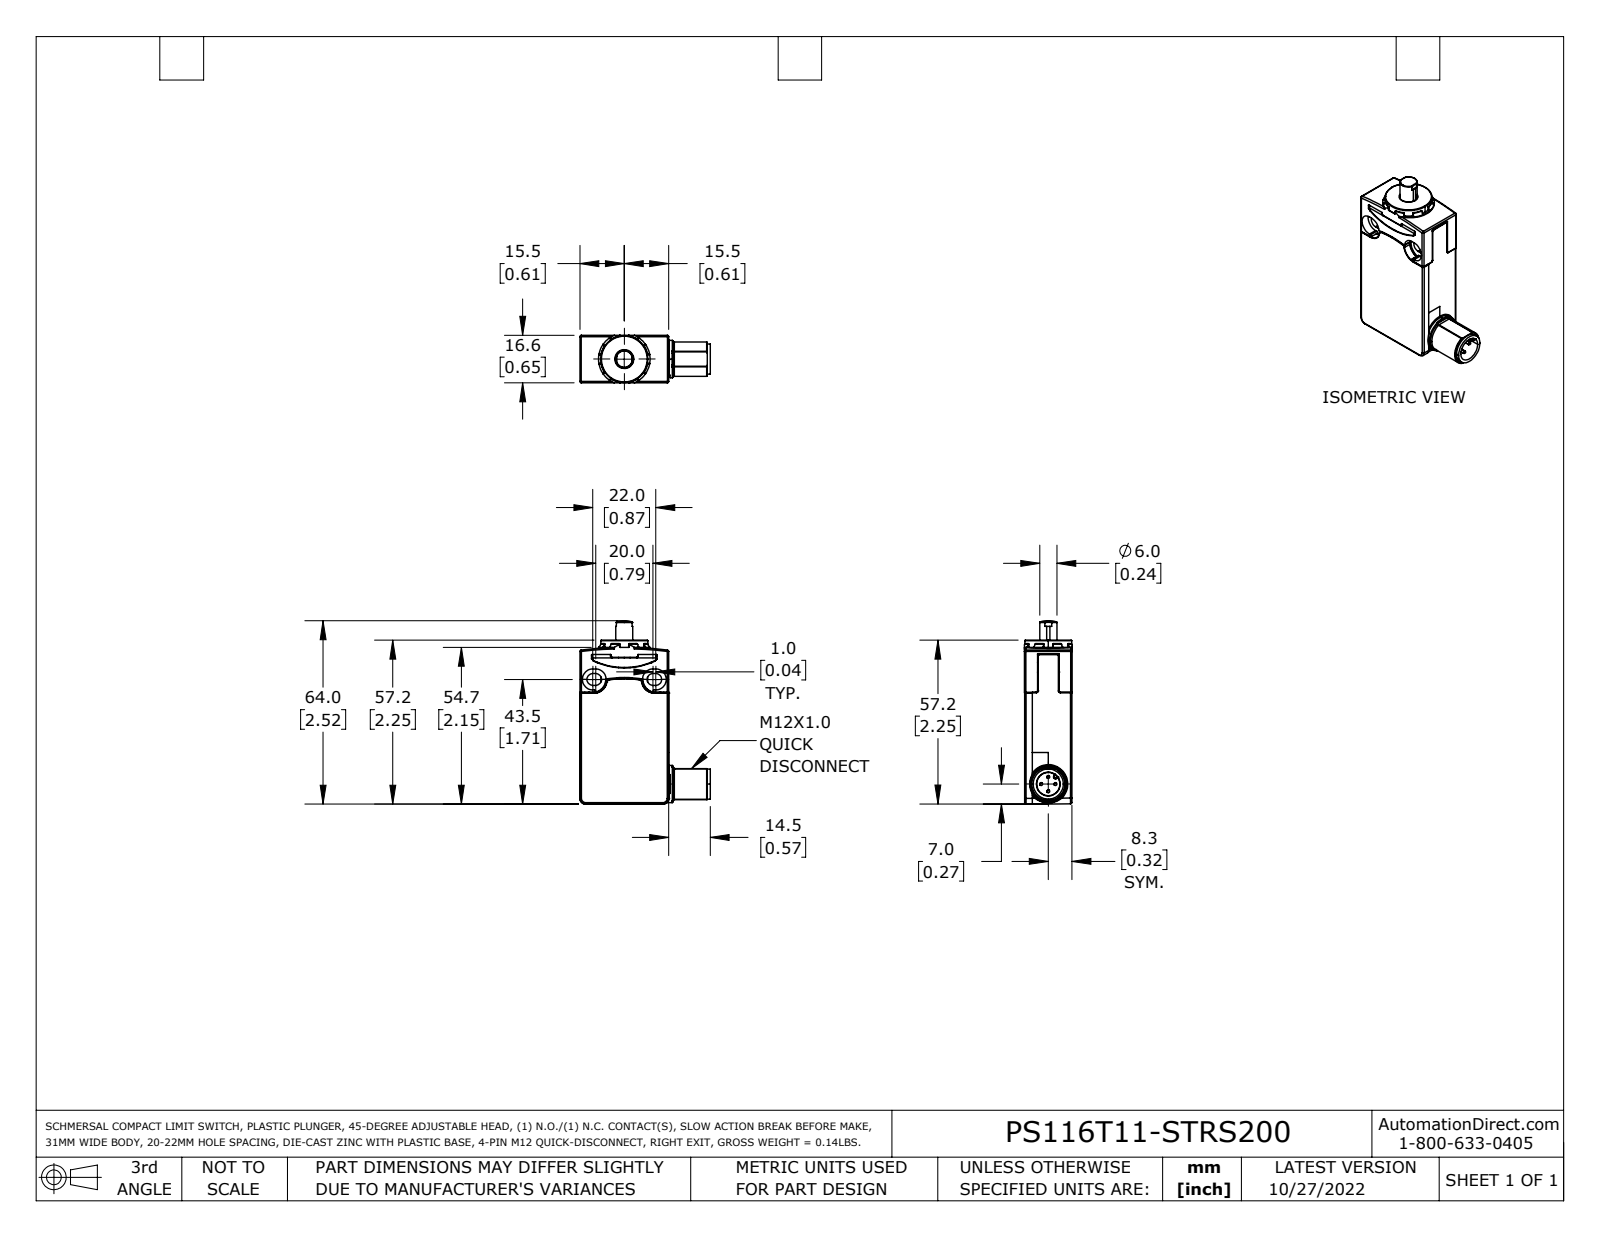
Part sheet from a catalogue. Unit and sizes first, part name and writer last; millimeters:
Units: millimetres
Overall size (bounding box): 64 × 45.5 × 16.6
Round holes (diameter × count): ⌀2 ×2, ⌀6.2 ×1, ⌀8.3 ×1, ⌀14.5 ×1
Round bosses / shafts (diameter × count): ⌀1 ×4, ⌀13 ×2, ⌀16.4 ×1, ⌀14.4 ×1, ⌀13.3 ×1, ⌀10.5 ×1, ⌀6 ×1
Partial cylindrical surfaces — rounded edges, fillets, slot ends (radius × count): R0.2 ×110, R0.1 ×67, R0.5 ×34, R0.4 ×10, R1 ×8, R2 ×5, R2.1 ×4, R3 ×4
Main face-to-face distances: 16.5, 16.6, 31, 3, 16.6, 4.5, 9, 5, 13.6, 2.9
Hole centre spacings: 41
Volume: 28 100 mm³ · Surface area: 10 760 mm²
Bodies: 1 solid, 875 faces (270 planar, 380 cylindrical, 225 other)
Part name (STEP PRODUCT): PS116T11-STRS200_Default
STEP written by: SolidWorks 2021 (CONFIG_CONTROL_DESIGN)
